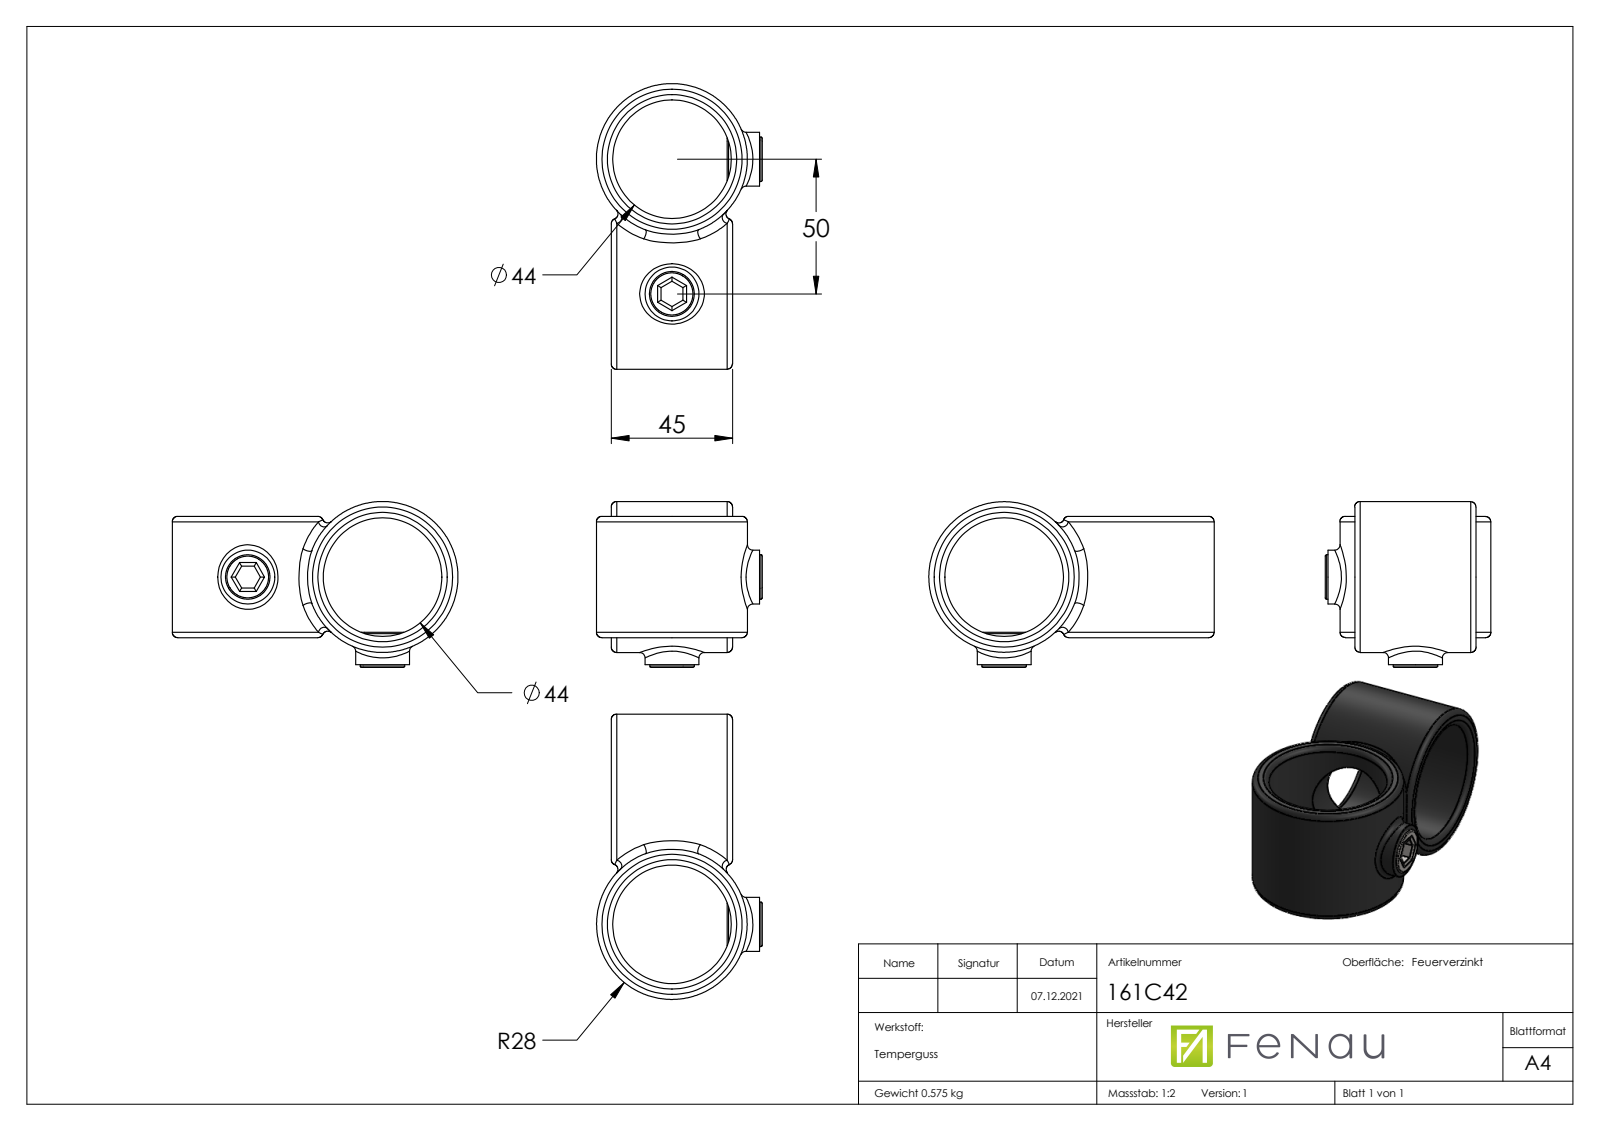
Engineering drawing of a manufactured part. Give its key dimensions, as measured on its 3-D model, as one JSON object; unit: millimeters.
{"part_name": "161-C42 Teil1; 161-C42; 161-C42 Teil2", "step_written_by": "SolidWorks 2018 (CONFIG_CONTROL_DESIGN)", "units": "millimeters", "bodies": {"solids": 3, "faces": 79, "planar": 22, "cylindrical": 35, "other": 22}, "overall_size": [106, 61.5, 61.5], "volume_mm3": 78463, "surface_area_mm2": 31420, "round_holes": [[15.25, 2], [44, 2], [30, 1]], "round_bosses_or_shafts": [[56, 2], [20, 2], [16.5, 2]], "partial_cylinders_radius": [[2, 24]], "face_to_face_distances": [45, 8.1, 10, 55, 26.55, 18.45, 1, 11, 13, 56], "hole_center_spacings": [50]}
